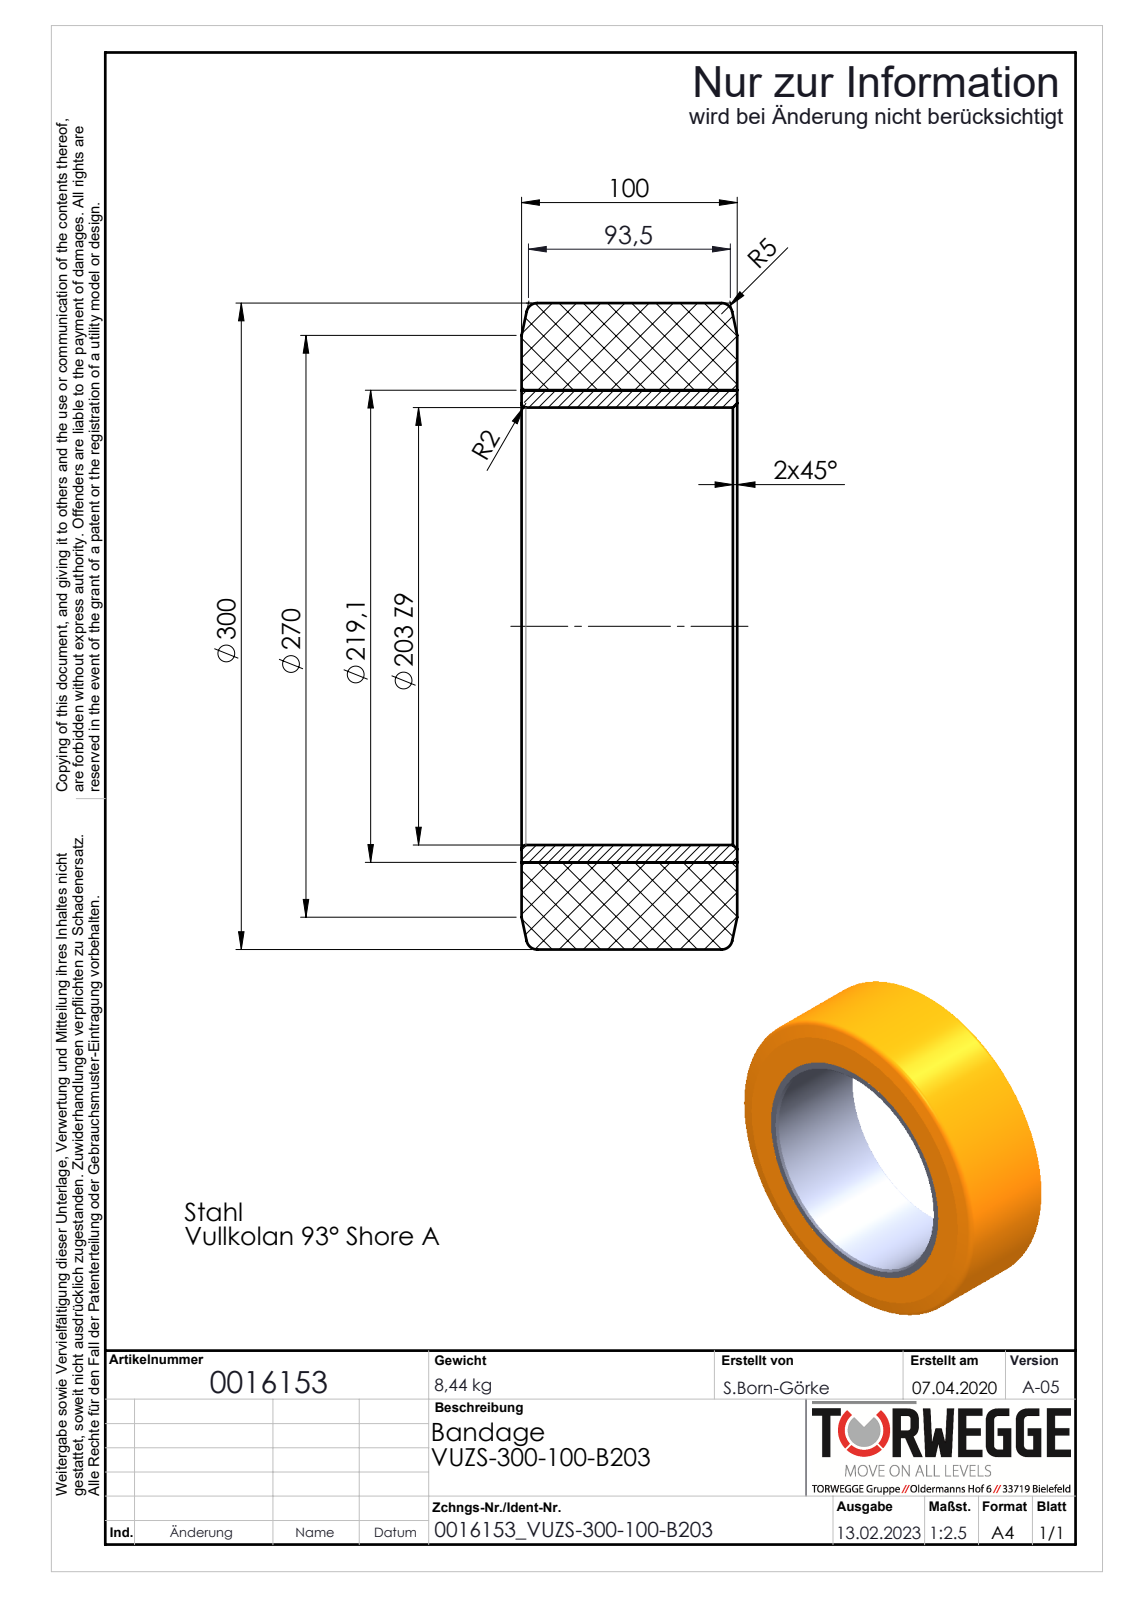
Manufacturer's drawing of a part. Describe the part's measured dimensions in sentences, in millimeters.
The part is named "0016153". Its 3-D file was written by "SolidWorks 2018 (AUTOMOTIVE_DESIGN)". It is 2 solids with 24 faces: 4 planar, 8 cylindrical and 12 other. Overall it measures 300 by 300 by 100 millimeters. Its volume is 3 781 000 cubic millimeters and its surface area 363 177 square millimeters. Round holes: 1 of diameter 203, 1 of diameter 219.1. Round bosses or shafts: 1 of diameter 300. The main face-to-face distances are 100.
